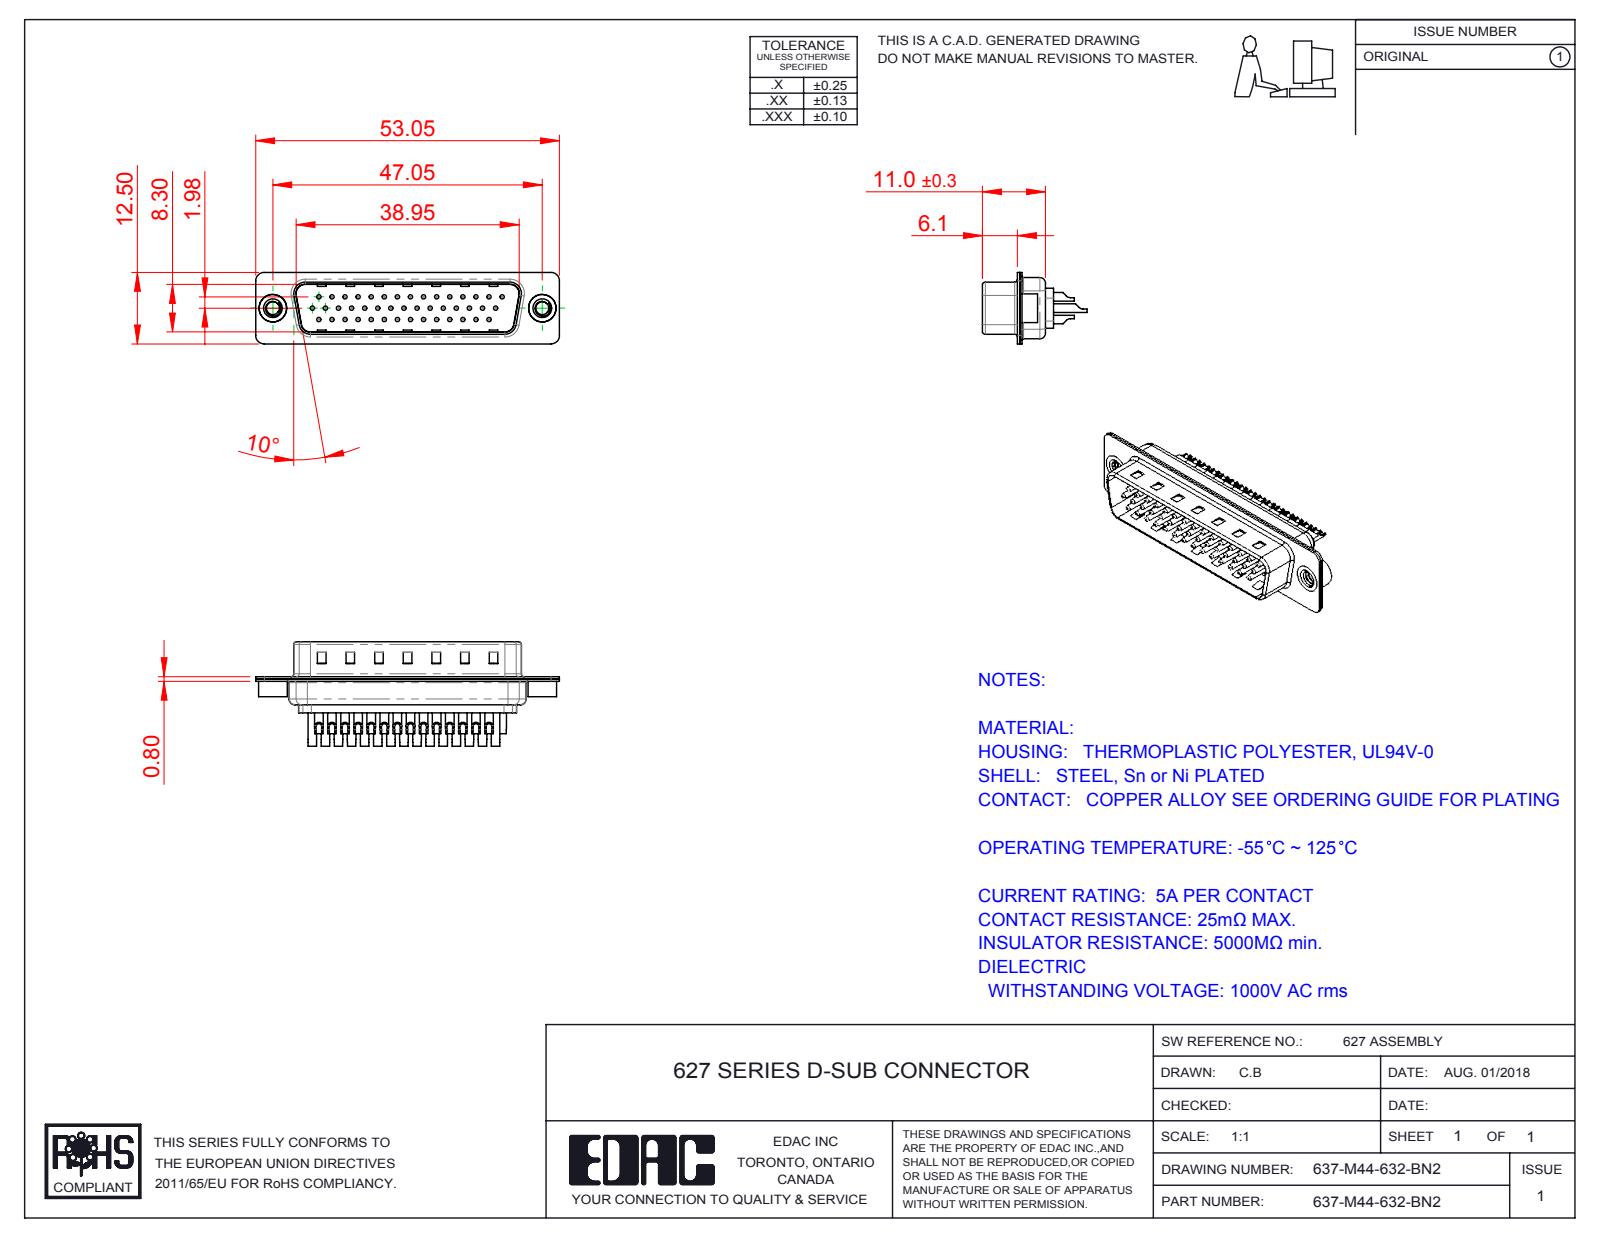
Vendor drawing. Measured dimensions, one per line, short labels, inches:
name: 637M Housing_44 Contacts; 637M Contact Row 3_32; 637M Contact Row 1_32; 637M Shell Rear_44 Contacts (+4 more)
written by: SolidWorks 2016 (CONFIG_CONTROL_DESIGN)
unit: in
bodies: 49 solids, 2004 faces (567 planar, 841 cylindrical, 596 other)
size: 2.089 × 0.719 × 0.492
volume: 0.181 in³; area: 13.97 in²
holes: 44× ⌀0.03, 44× ⌀0.039, 44× ⌀0.063, 44× ⌀0.079, 2× ⌀0.089, 2× ⌀0.157, 2× ⌀0.189
bosses: 44× ⌀0.059, 3× ⌀0.079, 3× ⌀0.03, 2× ⌀0.197, 2× ⌀0.193
rounds: 16× R0.059, 12× R0.079, 8× R0.02, 8× R0.063, 7× R0.039, 4× R0.01, 4× R0.024, 4× R0.026
face distances: 0.016, 0.031, 0.374, 0.358, 0.343, 0.39, 0.03, 0.014, 0.043, 0.047
hole spacings: 0.09, 0.156, 0.09, 0.18, 0.324, 0.27, 0.45, 0.59
